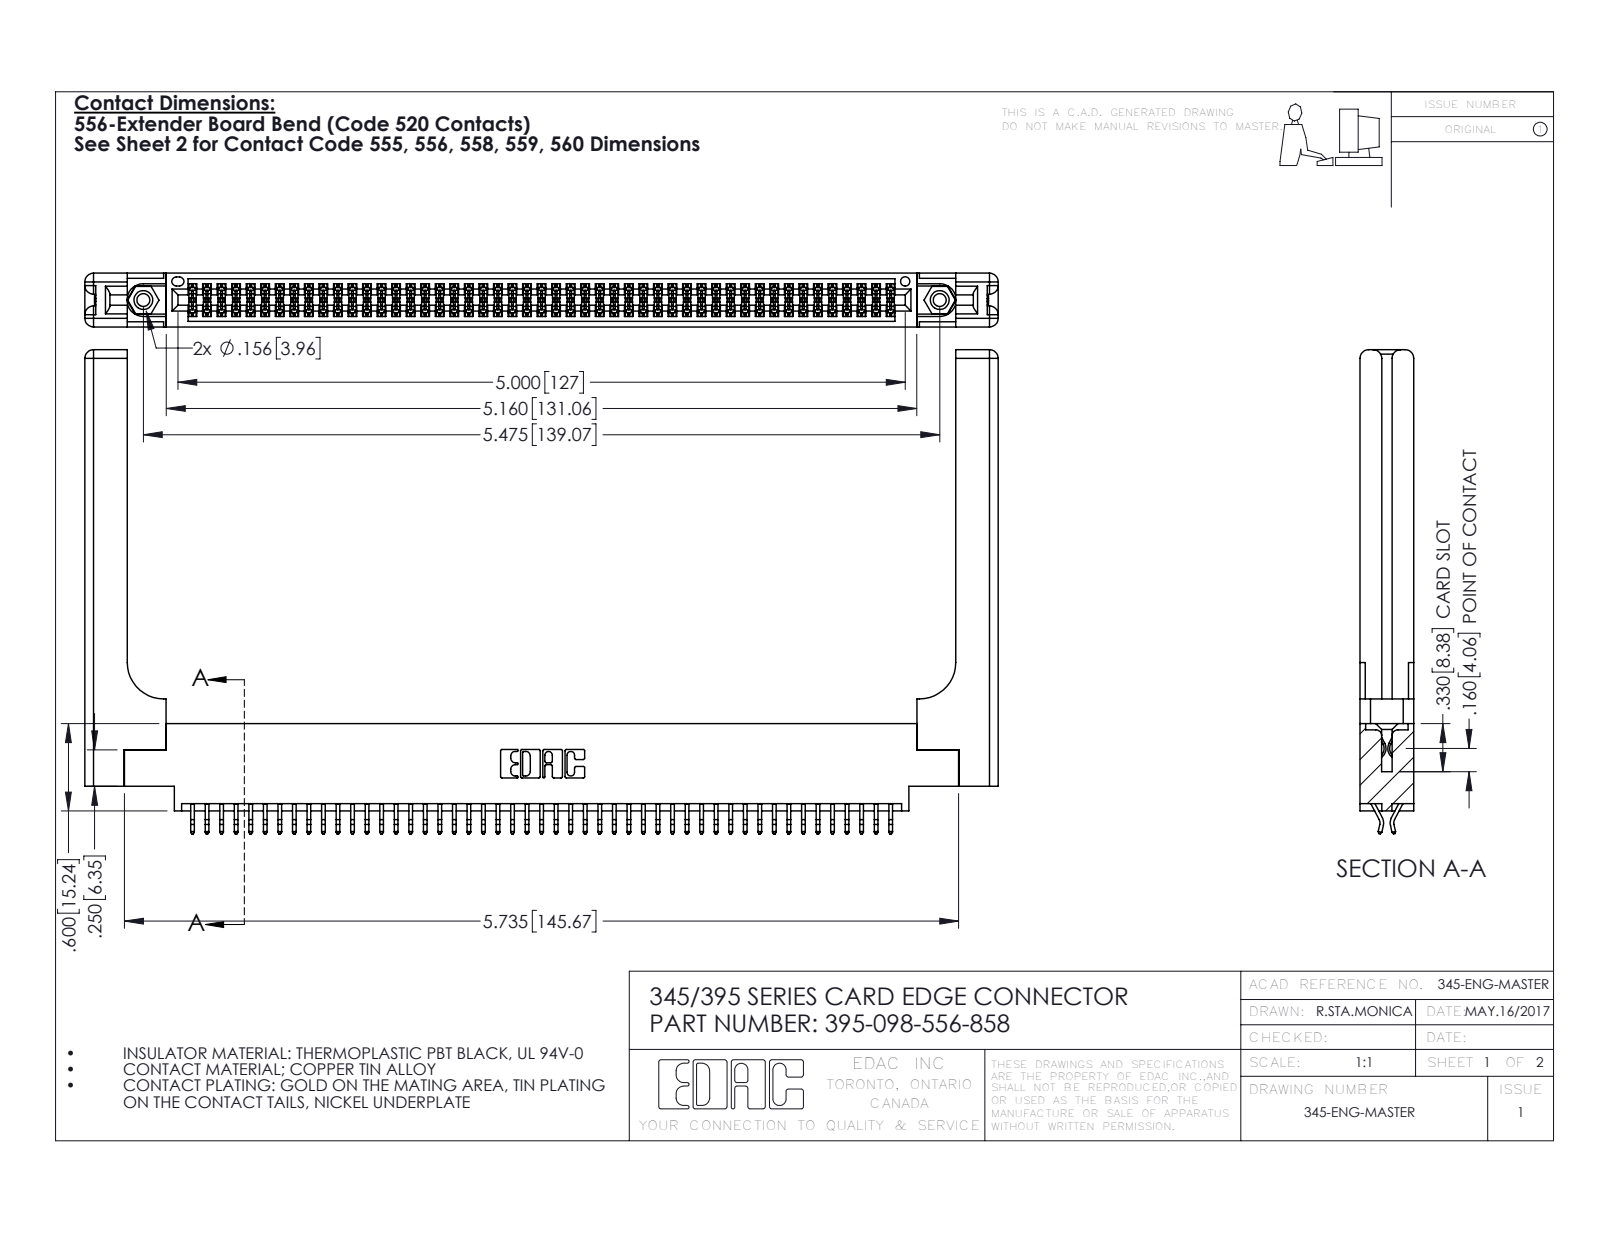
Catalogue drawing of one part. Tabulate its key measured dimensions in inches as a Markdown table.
| quantity | value |
| --- | --- |
| part name | 345-292-001_556 Tail; 395-098-556-858; 345-250-001_345-250-001-102; 345 Part_0.170 Offset - 0.156 Dia-TH (+1 more) |
| STEP written by | SolidWorks 2016 (CONFIG_CONTROL_DESIGN) |
| units | inches |
| bodies | 103 solids, 5874 faces (3858 planar, 1956 cylindrical, 60 other) |
| overall size | 6.279 × 3.327 × 0.37 |
| volume | 1.459 in³ |
| surface area | 43.52 in² |
| round holes (diameter × count) | 0.089 × 2, 0.125 × 2, 0.156 × 2, 0.064 × 1 |
| round bosses / shafts (diameter × count) | 0.155 × 2 |
| partial cylindrical surfaces (radius × count) | 0.006 × 147, 0.01 × 22, 0.06 × 16, 0.007 × 6, 0.031 × 6, 0.026 × 3, 0.01 × 2, 0.014 × 2 |
| main face-to-face distances | 0.072, 0.37, 0.298, 0.025, 0.098, 0.272, 0.2, 0.225, 0.148, 0.15 |
| hole center spacings | 0.27, 5.239, 5.475 |
